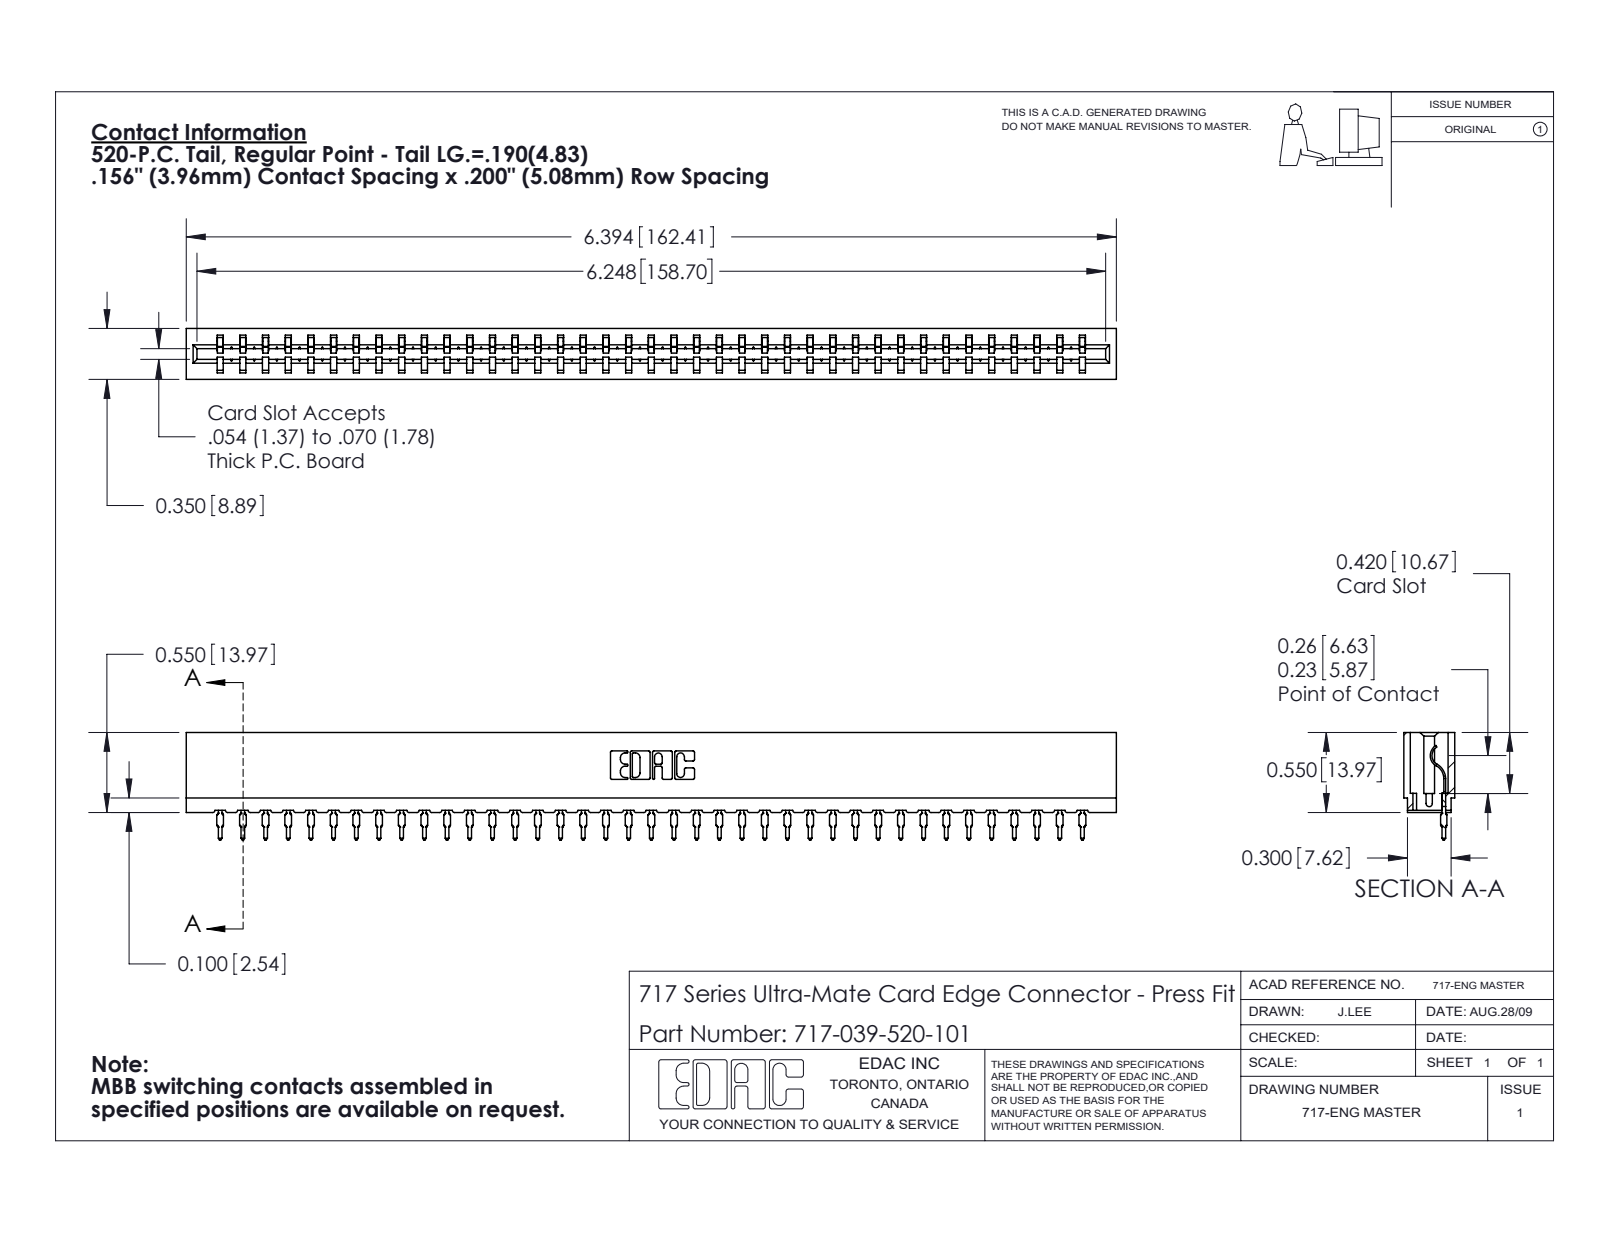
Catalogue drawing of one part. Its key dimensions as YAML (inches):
part_name: "717-039-520-101; 717 Part_Insulator Option - 06; 745-292-001_520"
step_written_by: "SolidWorks 2020 (CONFIG_CONTROL_DESIGN)"
units: inches
bodies: {solids: 40, faces: 4501, planar: 2706, cylindrical: 781, other: 1014}
overall_size: [6.394, 0.739, 0.35]
volume: 0.834
surface_area: 29.29
partial_cylinders:
  - {radius: 0.015, count: 78}
  - {radius: 0.021, count: 78}
  - {radius: 0.01, count: 22}
  - {radius: 0.007, count: 6}
  - {radius: 0.031, count: 6}
  - {radius: 0.005, count: 4}
  - {radius: 0.011, count: 4}
  - {radius: 0.026, count: 3}
face_to_face_distances: [0.212, 0.138, 0.35, 0.074, 0.045, 0.305, 0.093, 0.167, 0.025, 0.325]
